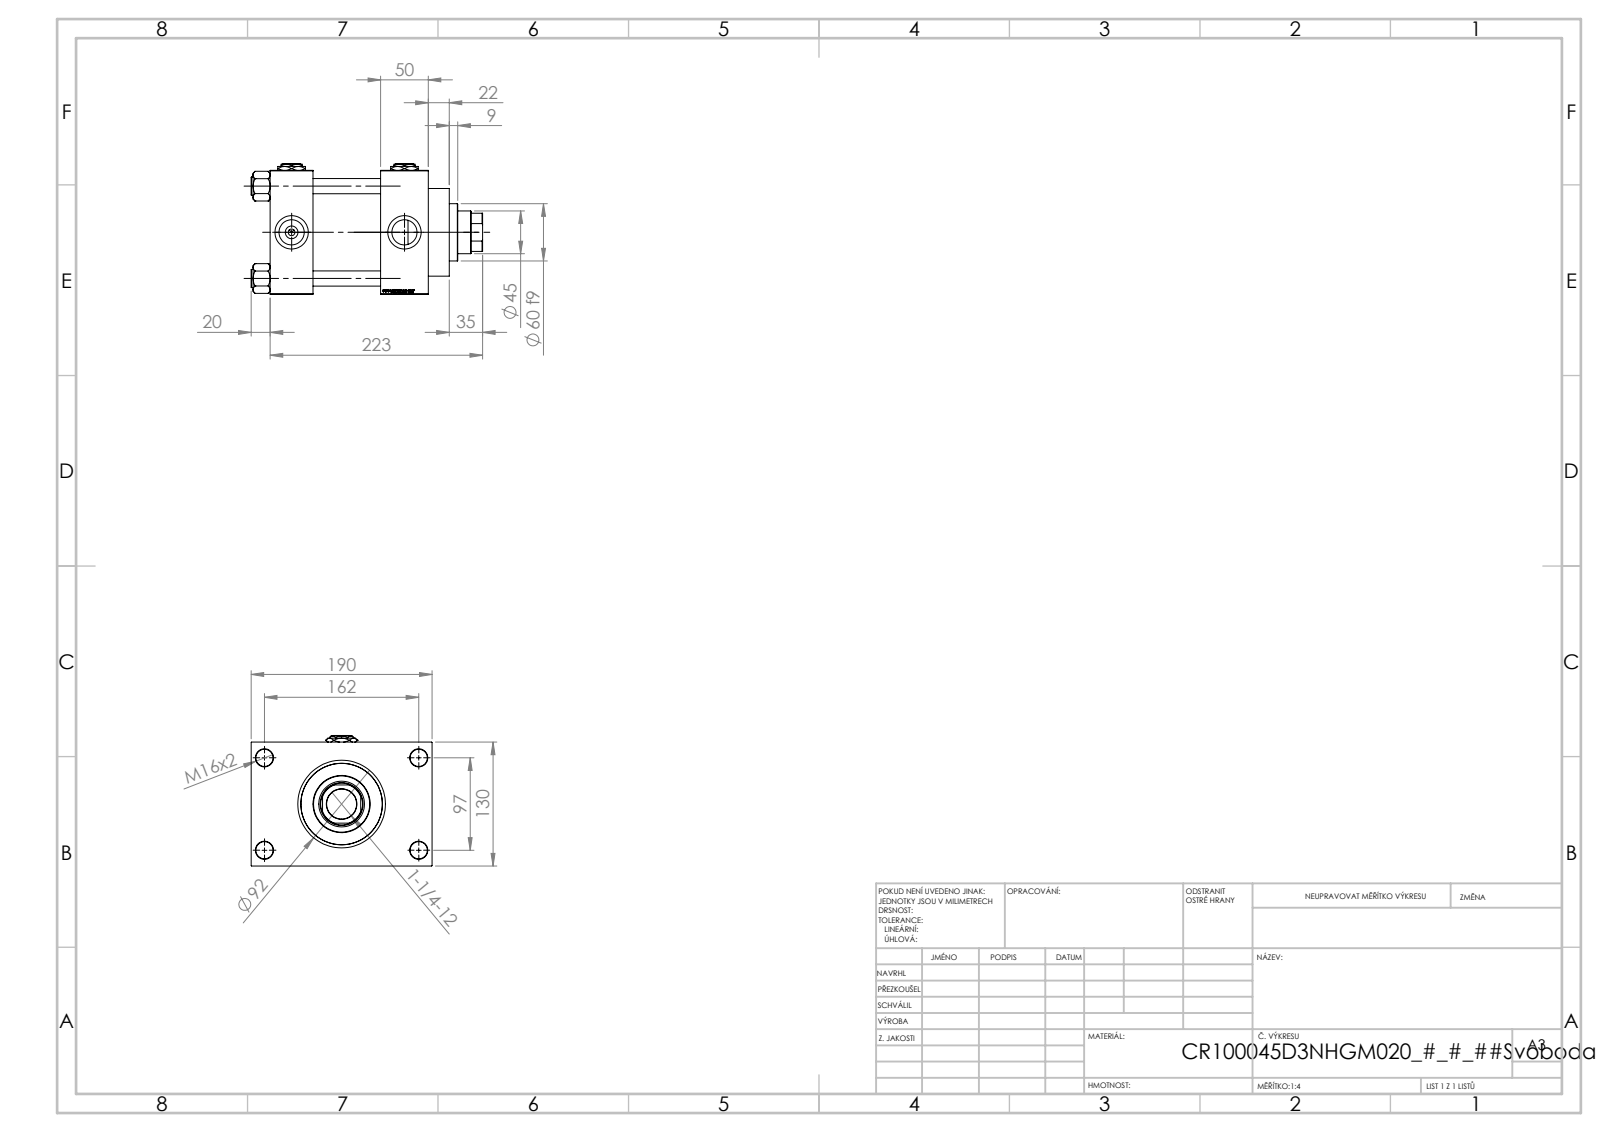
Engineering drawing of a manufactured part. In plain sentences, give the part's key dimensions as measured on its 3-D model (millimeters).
The part is named "V215CR_D_TYCINKA; V215CR_VCP_D; NUT_M5_D; Zatka_pro_OIL_PORT (+2 more)". Its 3-D file was written by "SolidWorks 2019 (CONFIG_CONTROL_DESIGN)". It is 13 solids with 1252 faces: 593 planar, 99 cylindrical and 560 other. Overall it measures 243 by 190 by 137 millimeters. Its volume is 2 576 000 cubic millimeters and its surface area 361 795 square millimeters. Round holes: 4 of diameter 16, 4 of diameter 18, 4 of diameter 26.44, 4 of diameter 35, 3 of diameter 7, 1 of diameter 31.5, 1 of diameter 45, 1 of diameter 48, 1 of diameter 76, 1 of diameter 85.5, 1 of diameter 100. Round bosses or shafts: 4 of diameter 19, 1 of diameter 106, 1 of diameter 92, 1 of diameter 60. Partial cylindrical surfaces (rounded edges, fillets, slot ends): 1 of radius 22. The main face-to-face distances are 45, 130, 116, 71, 166, 121, 50, 30, 160, 20. The hole center spacings are 32.55, 68.52, 94.41, 96.9, 102.27, 129.45, 161.73, 97.
